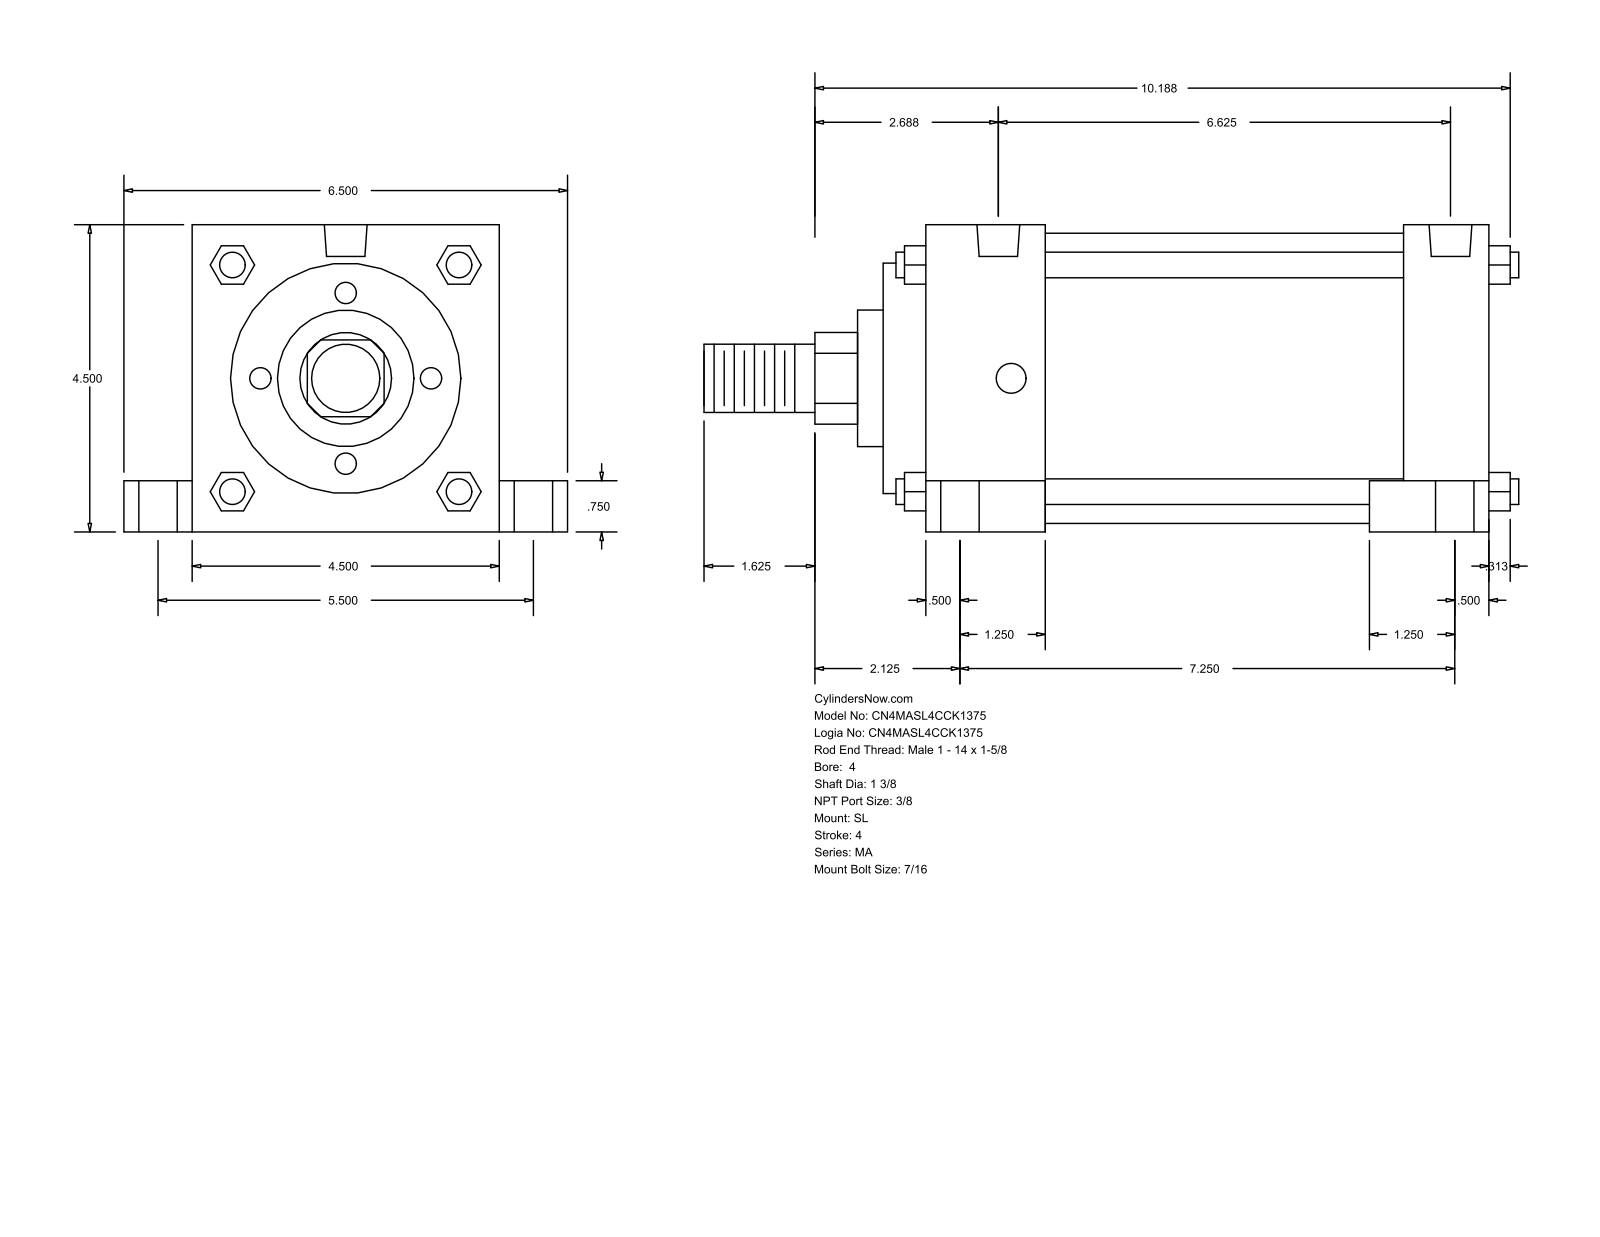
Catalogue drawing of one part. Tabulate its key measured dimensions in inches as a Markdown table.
| quantity | value |
| --- | --- |
| part name | MA_SL__0400_1.375 |
| STEP written by | GSSL Pune (CONFIG_CONTROL_DESIGN) |
| units | inches |
| bodies | 0 solids, 150 faces (113 planar, 37 cylindrical, 0 other) |
| overall size | 11.937 × 6.5 × 4.5 |
| round holes (diameter × count) | 0.437 × 4, 0.563 × 4, 0.813 × 4, 0.627 × 2 |
| round bosses / shafts (diameter × count) | 0.375 × 4, 4.25 × 1, 3.375 × 1, 2 × 1, 1.375 × 1, 1 × 1 |
| partial cylindrical surfaces (radius × count) | 0.672 × 1 |
| main face-to-face distances | 4.5, 8.25, 6.5, 5.25, 8.875, 0.625, 2.375, 1.75, 7.625, 7 |
| hole center spacings | 2.751, 2.761, 2.807, 2.85, 5.5, 6.25, 7.057, 7.231 |
